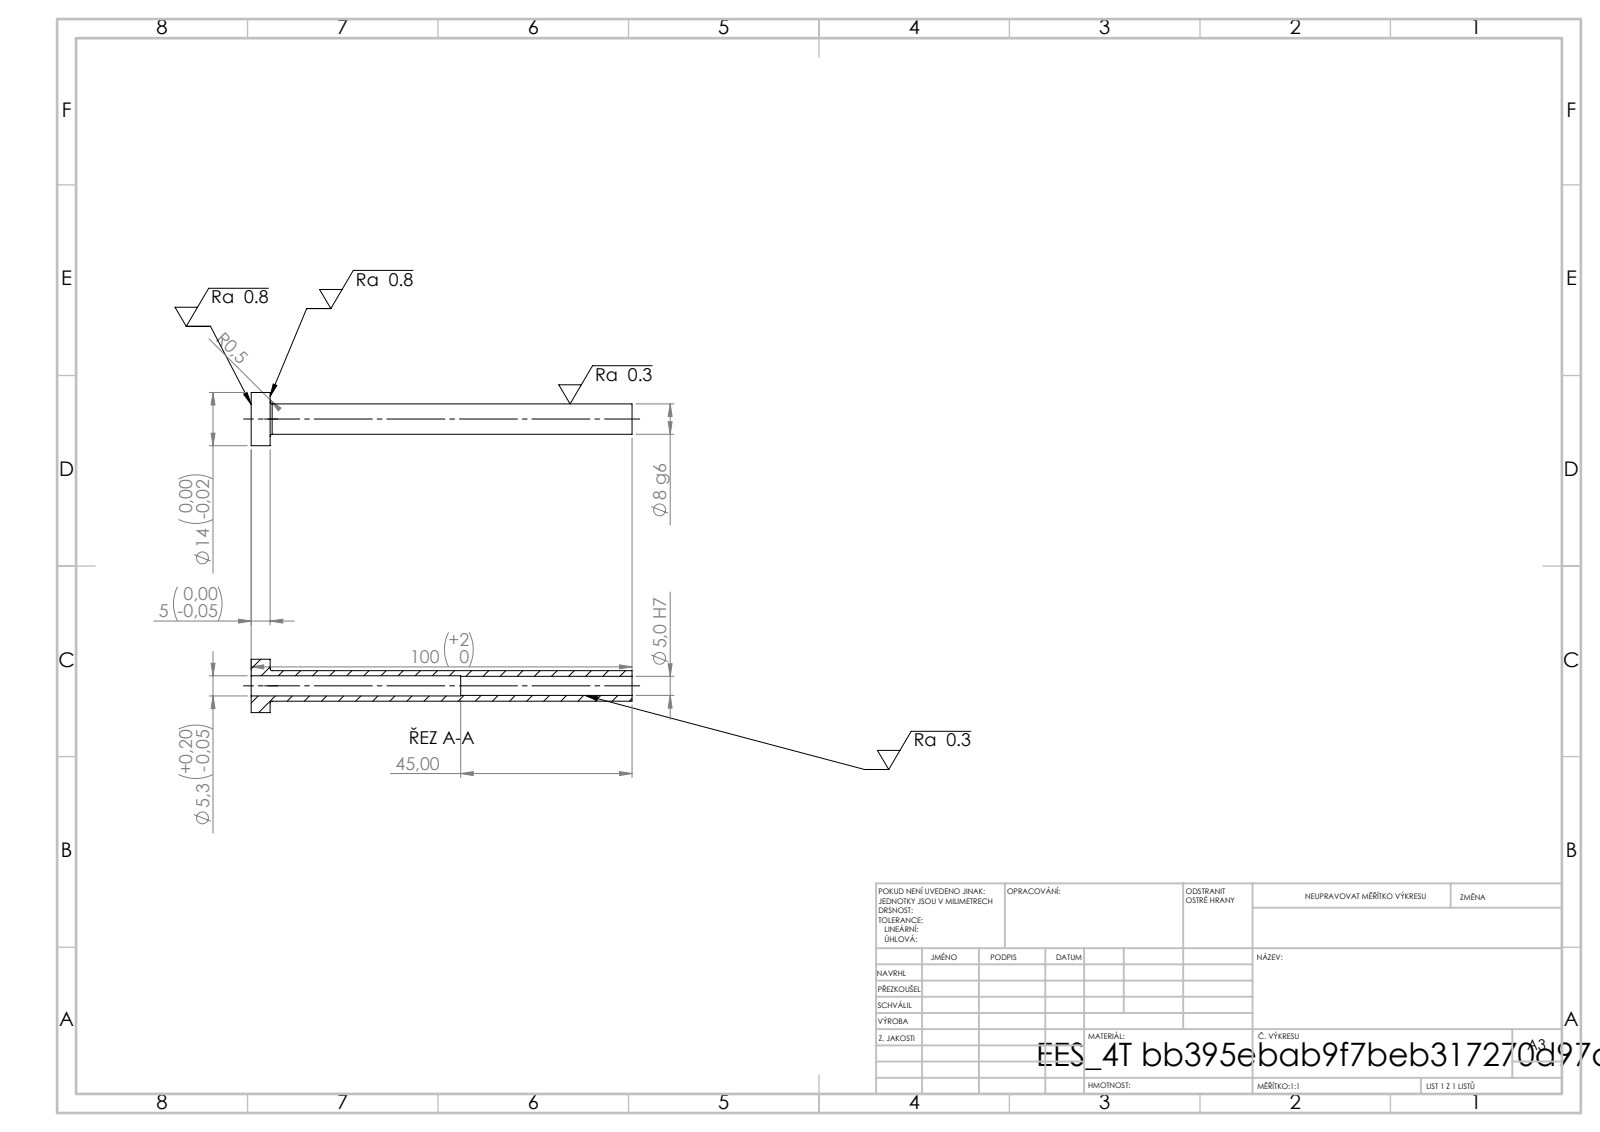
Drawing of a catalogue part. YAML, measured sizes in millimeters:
step_written_by: "SolidWorks 2019 (CONFIG_CONTROL_DESIGN)"
units: millimeters
bodies: {solids: 1, faces: 14, planar: 4, cylindrical: 8, other: 2}
overall_size: [100, 14, 14]
volume: 3449
surface_area: 4493
round_holes:
  - {diameter: 5, count: 1}
  - {diameter: 5.3, count: 1}
round_bosses_or_shafts:
  - {diameter: 14, count: 1}
  - {diameter: 8, count: 1}
face_to_face_distances: [5, 100, 95, 55, 50, 45]
